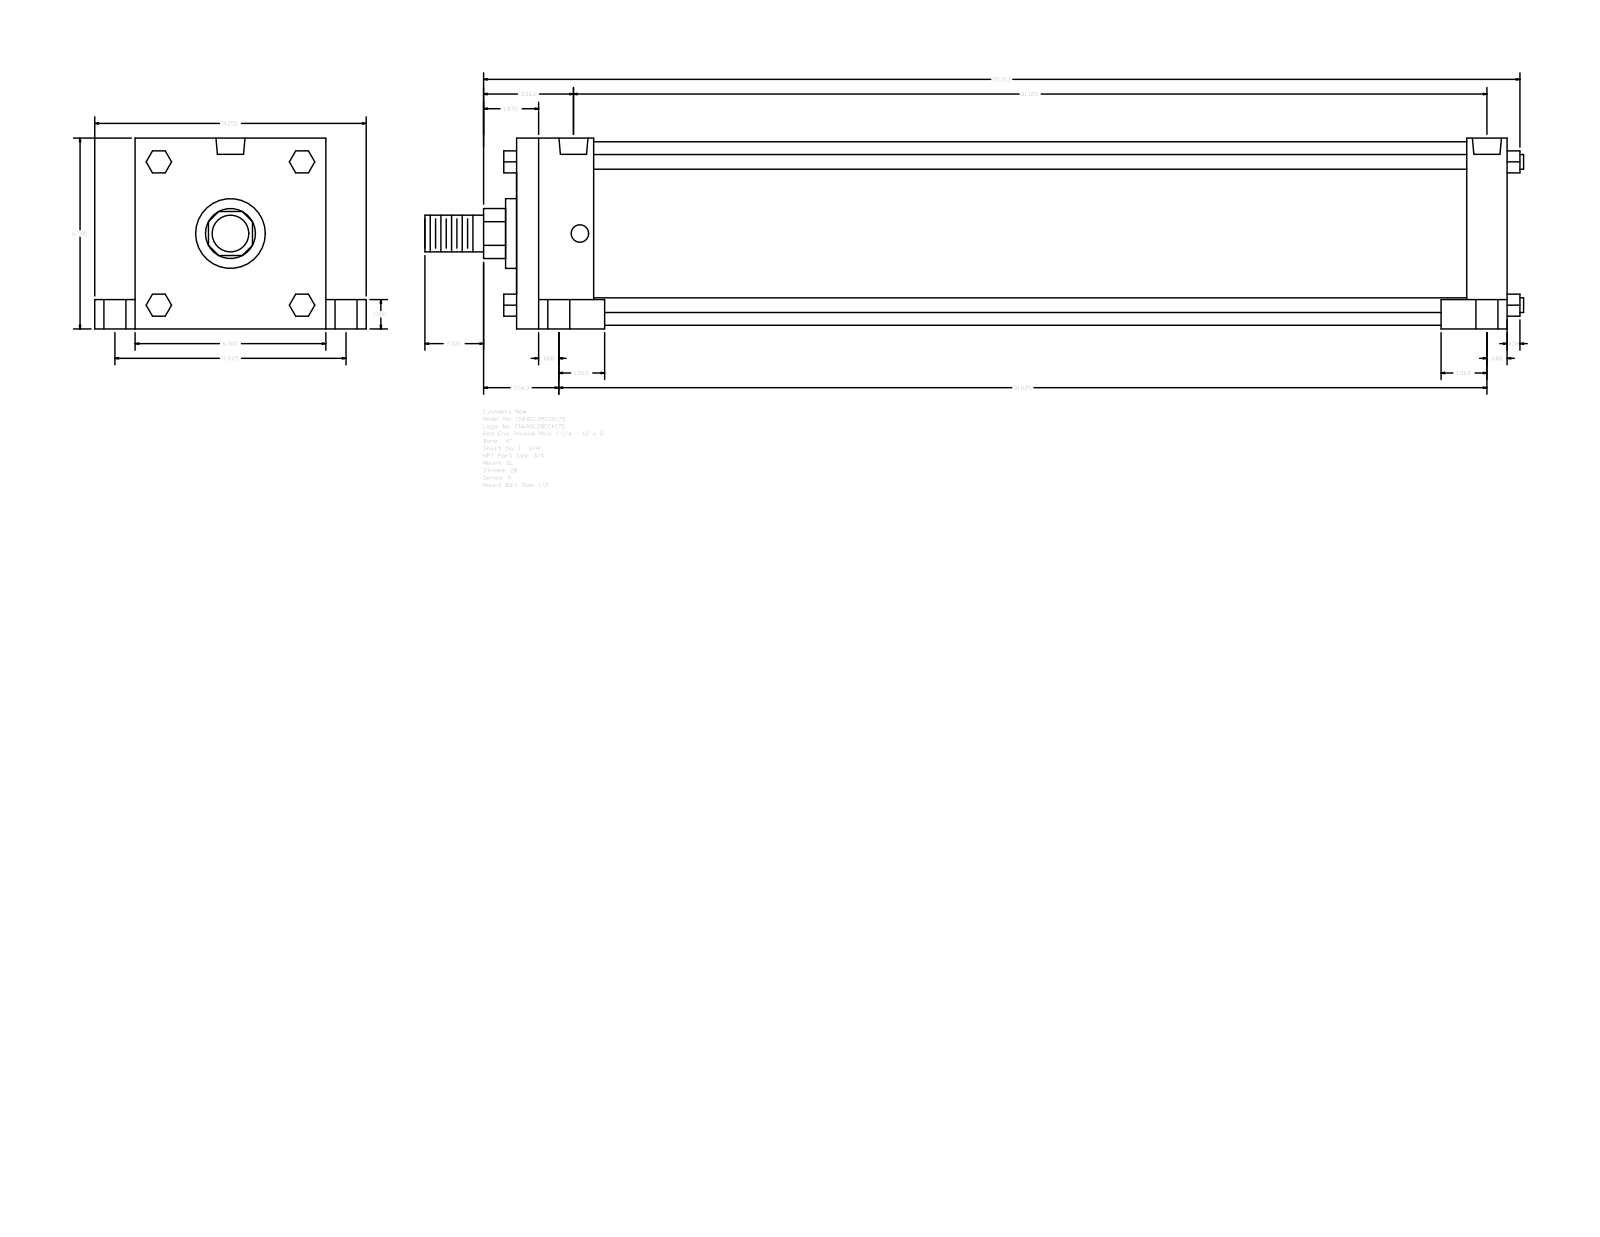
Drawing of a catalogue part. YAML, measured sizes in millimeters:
part_name: "A_SL__0600_1.75"
step_written_by: "GSSL Pune (CONFIG_CONTROL_DESIGN)"
units: millimeters
bodies: {solids: 0, faces: 150, planar: 114, cylindrical: 36, other: 0}
overall_size: [950.91, 234.95, 165.1]
round_holes:
  - {diameter: 15.08, count: 4}
  - {diameter: 19.05, count: 4}
  - {diameter: 25.4, count: 4}
  - {diameter: 25.12, count: 2}
round_bosses_or_shafts:
  - {diameter: 12.7, count: 4}
  - {diameter: 158.75, count: 1}
  - {diameter: 60.33, count: 1}
  - {diameter: 44.45, count: 1}
  - {diameter: 31.75, count: 1}
partial_cylinders:
  - {radius: 21.63, count: 1}
face_to_face_distances: [165.1, 857.26, 66.68, 790.58, 822.33, 755.65, 34.93, 25.4, 139.7, 34.92]
hole_center_spacings: [5.56, 100.01, 100.16, 100.81, 101.66, 200.02, 779.45, 785.01]
